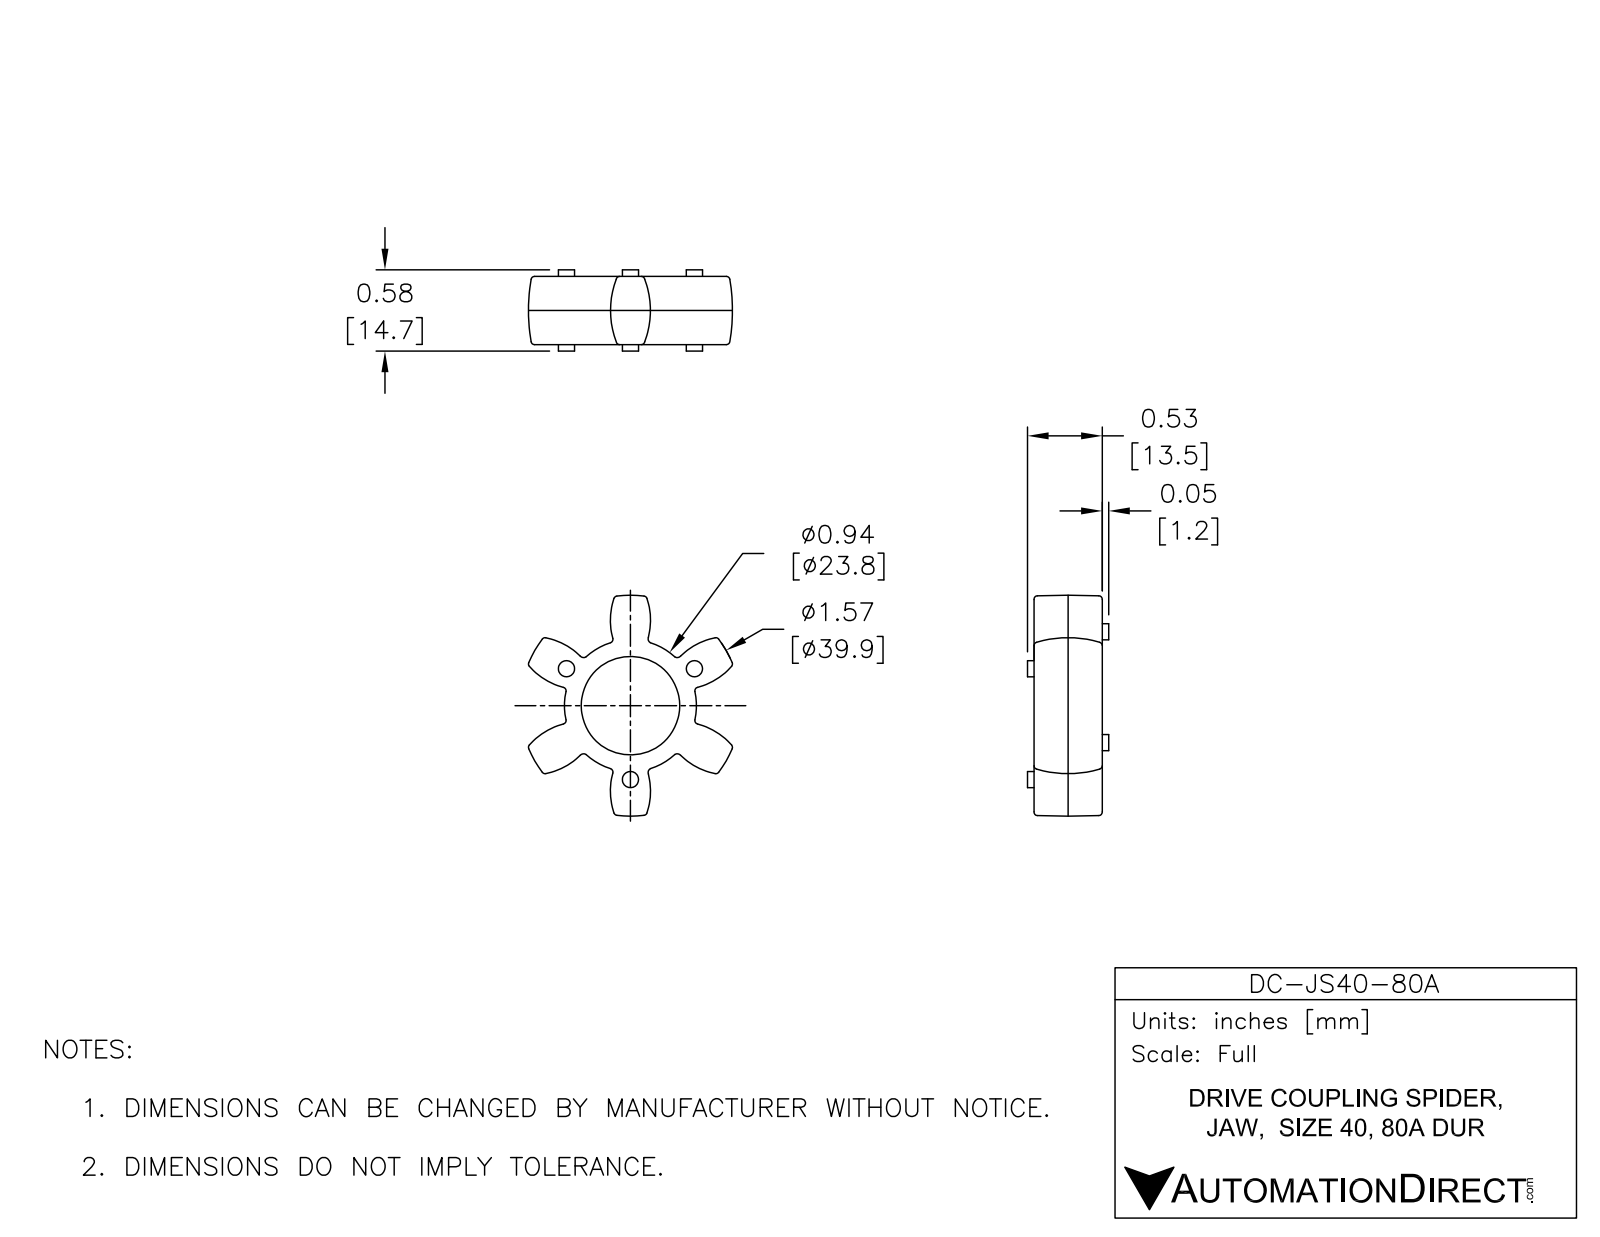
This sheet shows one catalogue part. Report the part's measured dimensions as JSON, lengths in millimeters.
{"part_name": "DC-JS40-80A", "step_written_by": "SolidWorks 2015 (AUTOMOTIVE_DESIGN)", "units": "millimeters", "bodies": {"solids": 1, "faces": 218, "planar": 8, "cylindrical": 14, "other": 196}, "overall_size": [39.88, 36.86, 14.66], "volume_mm3": 6394, "surface_area_mm2": 3734, "round_holes": [[17.78, 1]], "round_bosses_or_shafts": [[2.92, 6]], "face_to_face_distances": [12.32, 1.17, 13.49, 14.66]}
